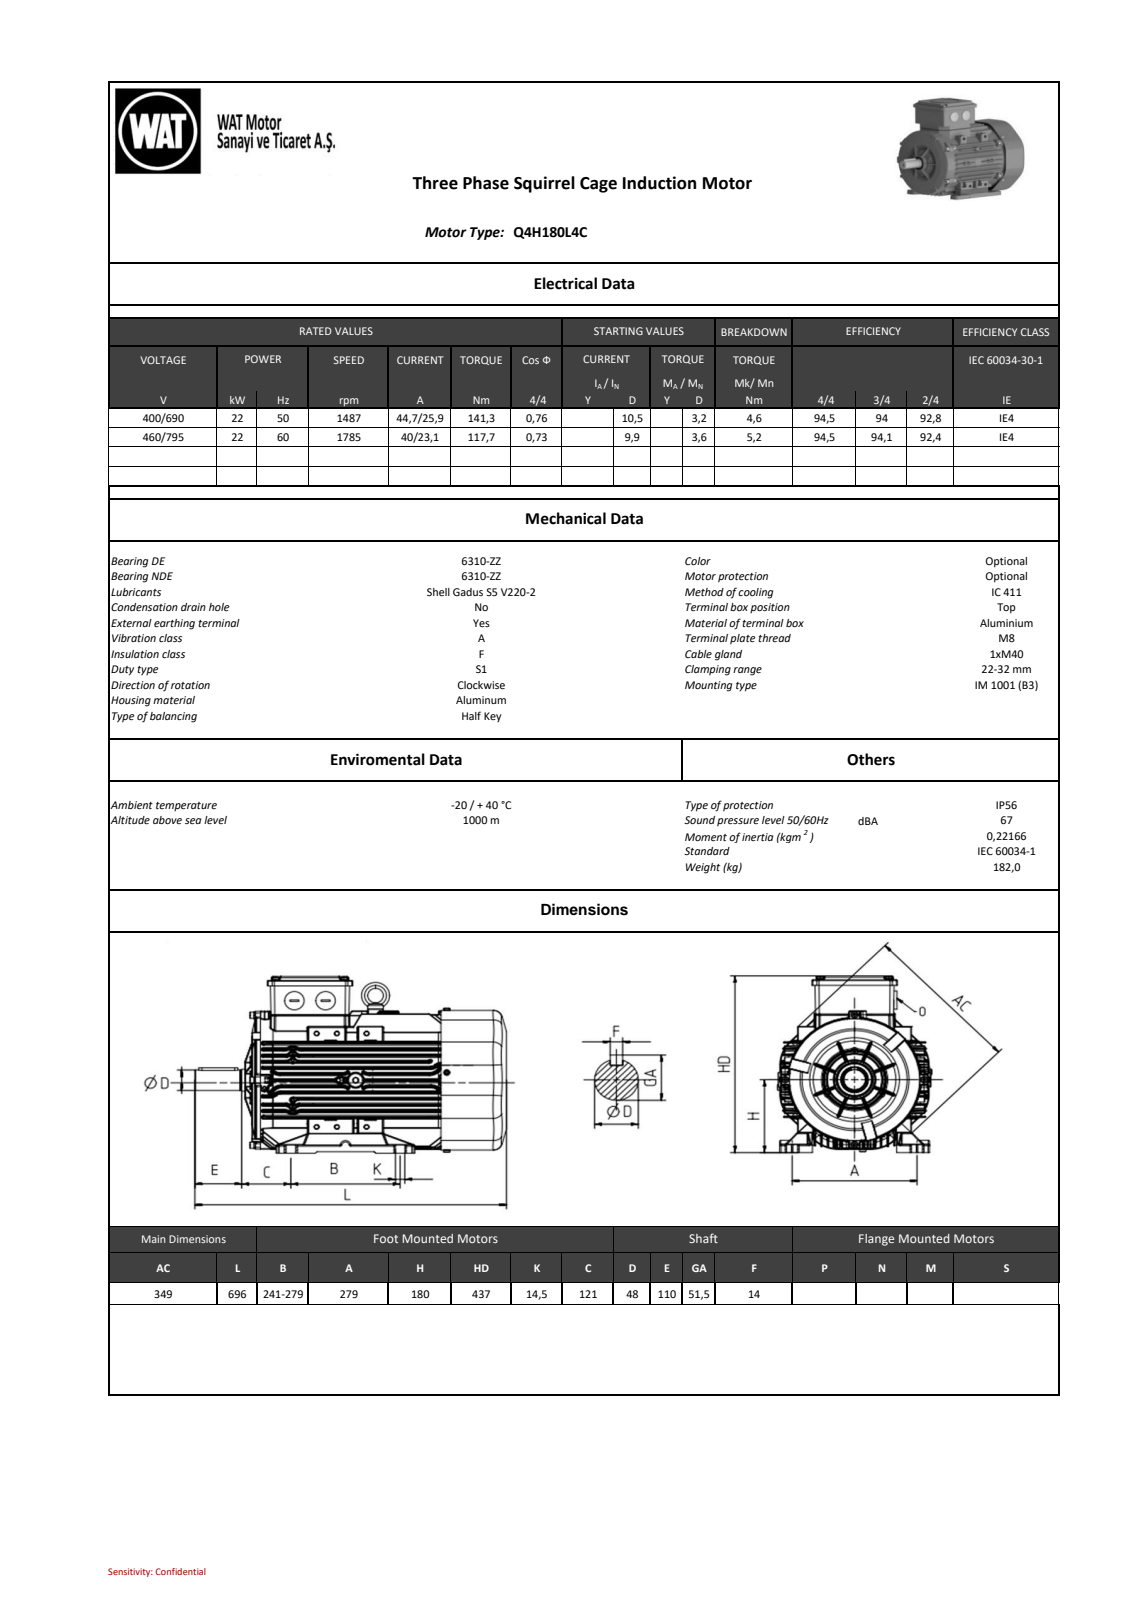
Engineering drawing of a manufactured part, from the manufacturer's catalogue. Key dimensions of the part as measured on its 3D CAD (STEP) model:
Part name (STEP PRODUCT): 001_objects
STEP written by: SIEMENS PLM Software NX2206.8101 (AP203_CONFIGURATION_CONTROLLED_3D_DESIGN_OF_MECHANICAL_PARTS_AND_ASSEMBLIES_MIM_LF)
Units: millimetres
Bodies: 0 solids, 7917 faces (2265 planar, 3079 cylindrical, 2573 other)
Overall size (bounding box): 696 × 433 × 358.05
Round holes (diameter × count): ⌀25.05 ×2, ⌀8 ×1, ⌀14 ×1, ⌀17 ×1, ⌀80 ×1
Round bosses / shafts (diameter × count): ⌀18.1 ×4, ⌀16 ×4, ⌀14.8 ×4, ⌀13 ×4, ⌀12 ×4, ⌀9.5 ×4, ⌀46 ×2, ⌀25 ×2
Partial cylindrical surfaces — rounded edges, fillets, slot ends (radius × count): R2 ×755, R1 ×705, R0.5 ×82, R5 ×57, R8 ×24, R1 ×20, R4 ×19, R0.96 ×16
Main face-to-face distances: 1.2, 5, 16.21, 32.48, 16.27, 171.05, 173.83, 141.35, 157.62, 157.07
Hole centre spacings: 342
